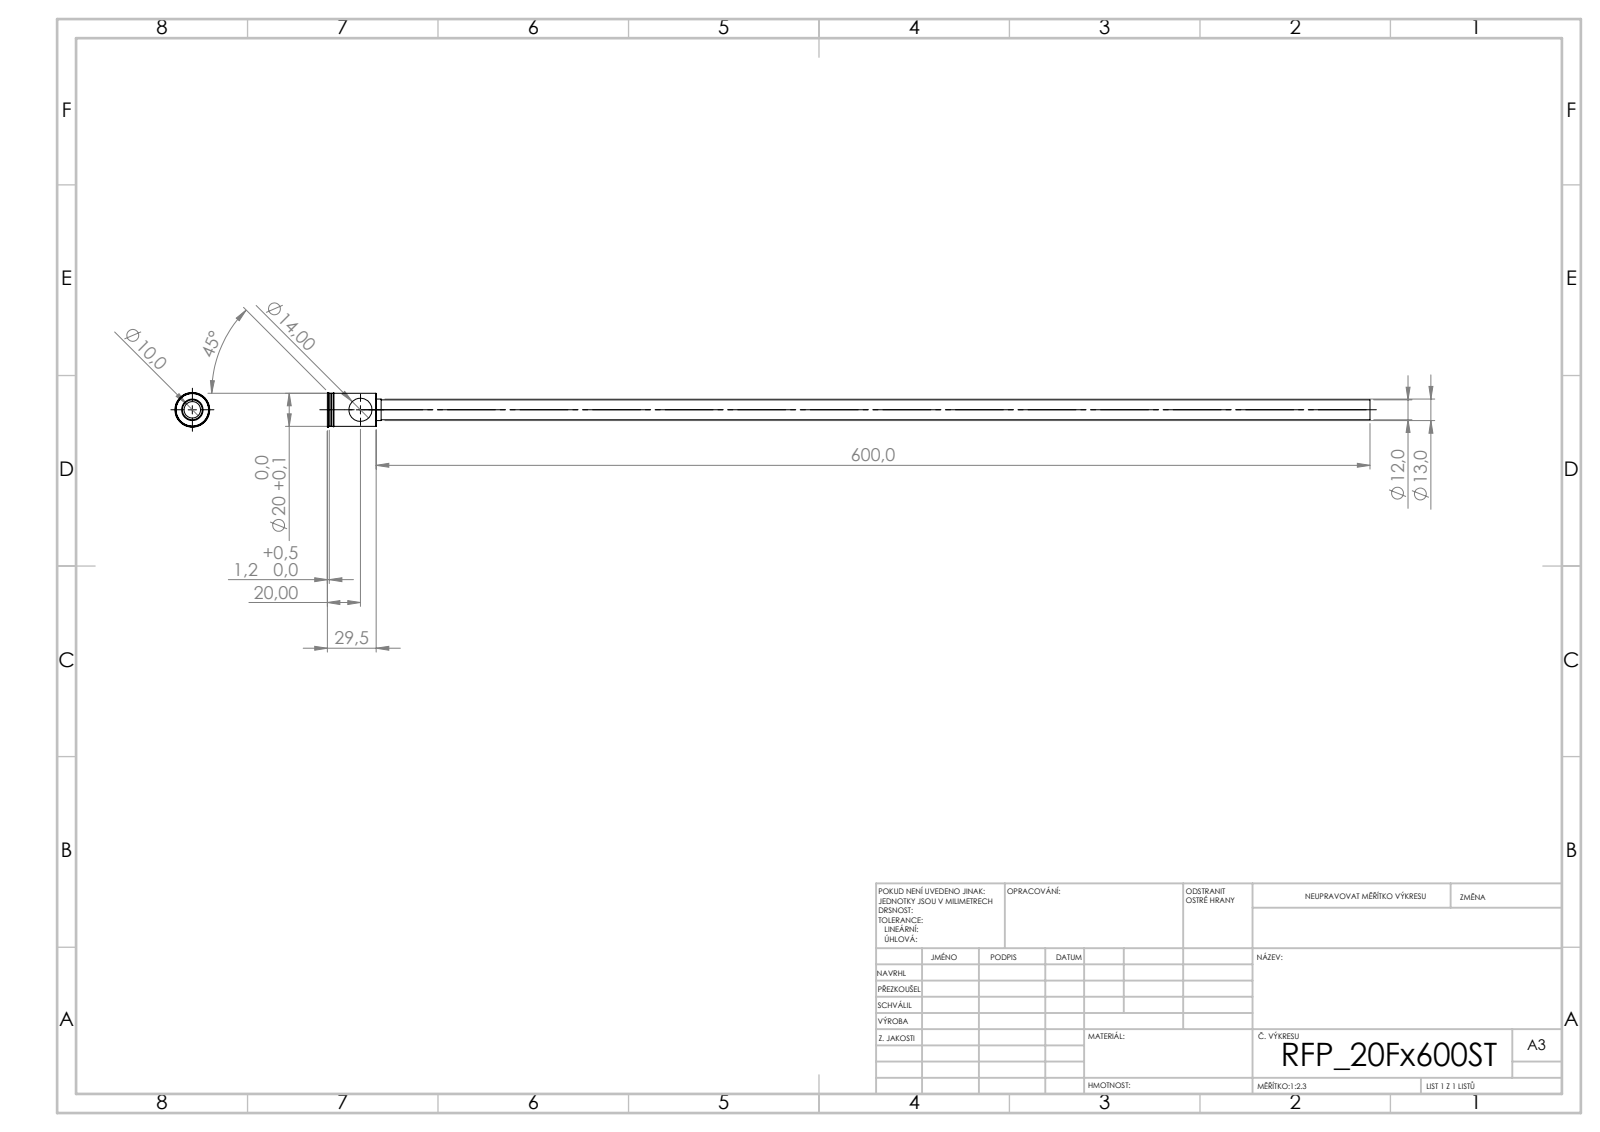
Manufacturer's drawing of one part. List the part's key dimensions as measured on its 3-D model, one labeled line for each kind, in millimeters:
STEP written by: SolidWorks 2019 (CONFIG_CONTROL_DESIGN)
Units: millimetres
Bodies: 1 solid, 44 faces (20 planar, 16 cylindrical, 8 other)
Overall size (bounding box): 629.5 × 21 × 21
Volume: 26 573 mm³ · Surface area: 44 528 mm²
Round holes (diameter × count): ⌀10 ×1, ⌀14 ×1
Round bosses / shafts (diameter × count): ⌀21 ×1, ⌀20 ×1, ⌀13 ×1, ⌀12 ×1
Main face-to-face distances: 27.5, 2, 29.5, 15.4, 600, 627.5, 629.5, 0.5, 597, 3
